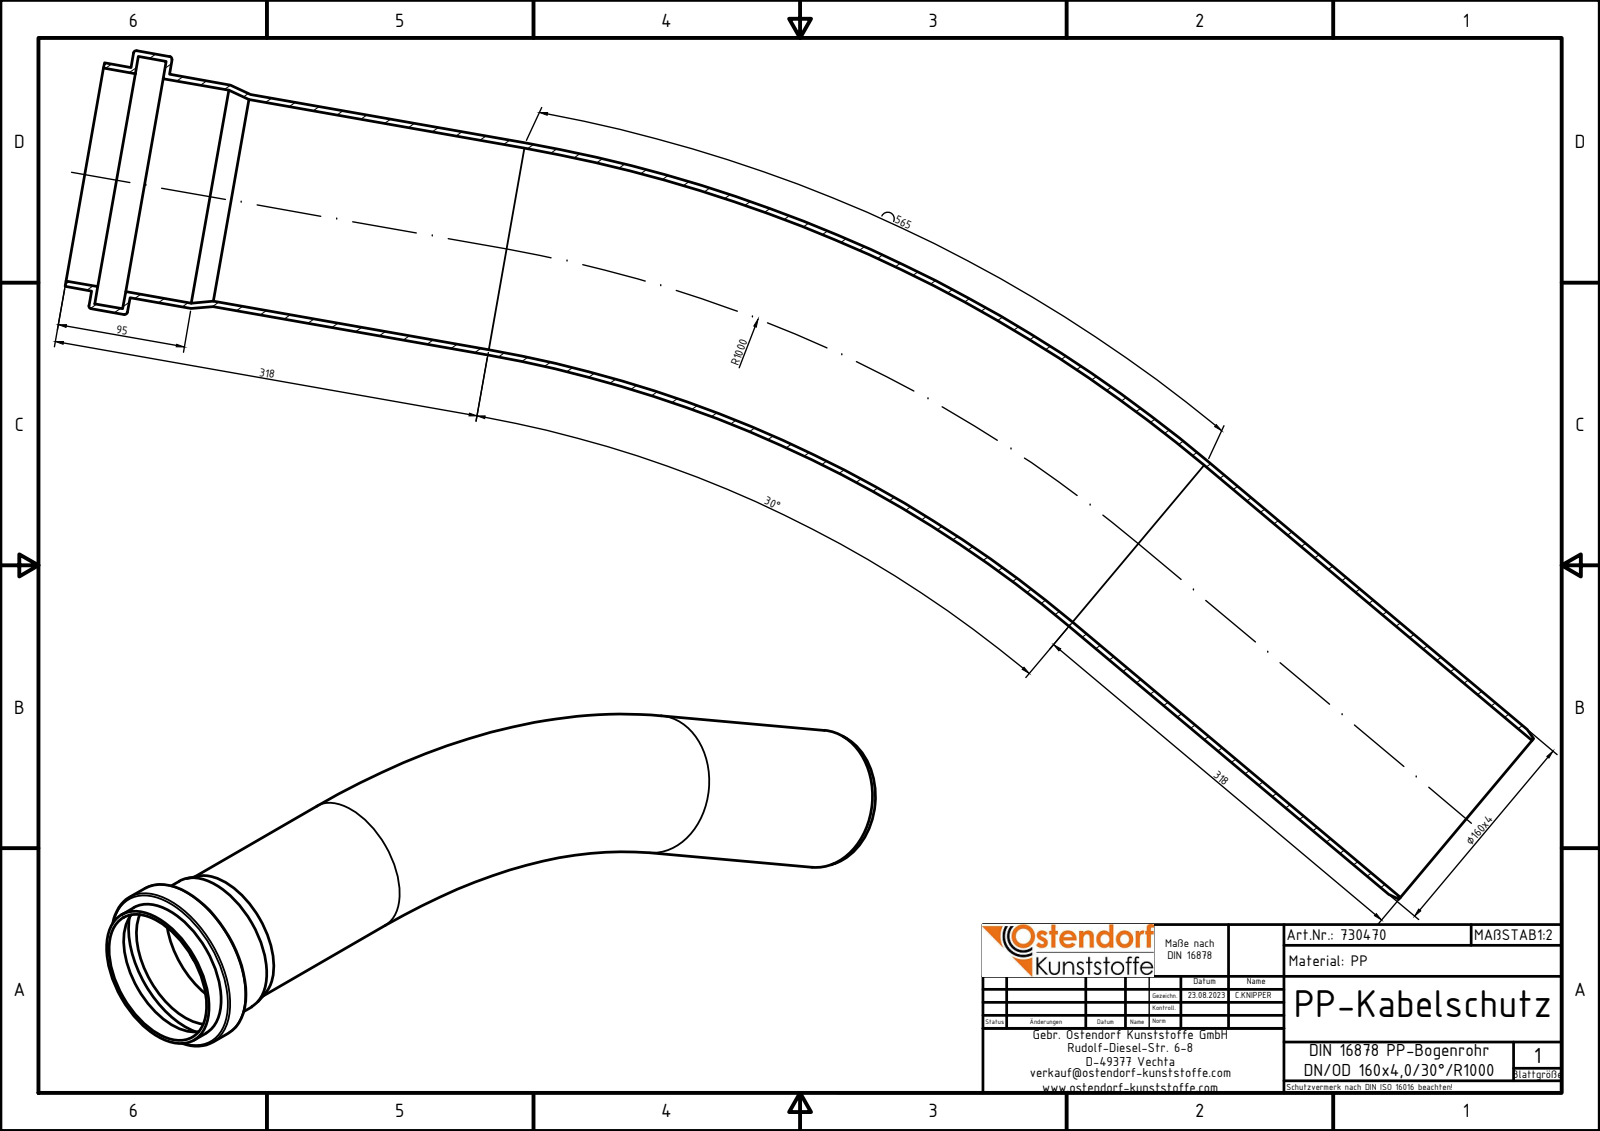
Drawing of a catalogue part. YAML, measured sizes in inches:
part_name: "PP-Bogenrohr_160x40_R1000_30_SM_34866_730470"
step_written_by: "Autodesk Inventor 2024 (AUTOMOTIVE_DESIGN)"
units: inches
bodies: {solids: 1, faces: 23, planar: 6, cylindrical: 10, other: 7}
overall_size: [44.58, 18.018, 7.657]
volume: 143.2
surface_area: 1826
round_holes:
  - {diameter: 5.984, count: 2}
  - {diameter: 6.319, count: 1}
  - {diameter: 7.343, count: 1}
round_bosses_or_shafts:
  - {diameter: 6.299, count: 2}
  - {diameter: 7.657, count: 1}
  - {diameter: 6.634, count: 1}
face_to_face_distances: [0.157, 0.984, 0.827, 1.142, 0.787, 0.945, 1.772, 1.929]
